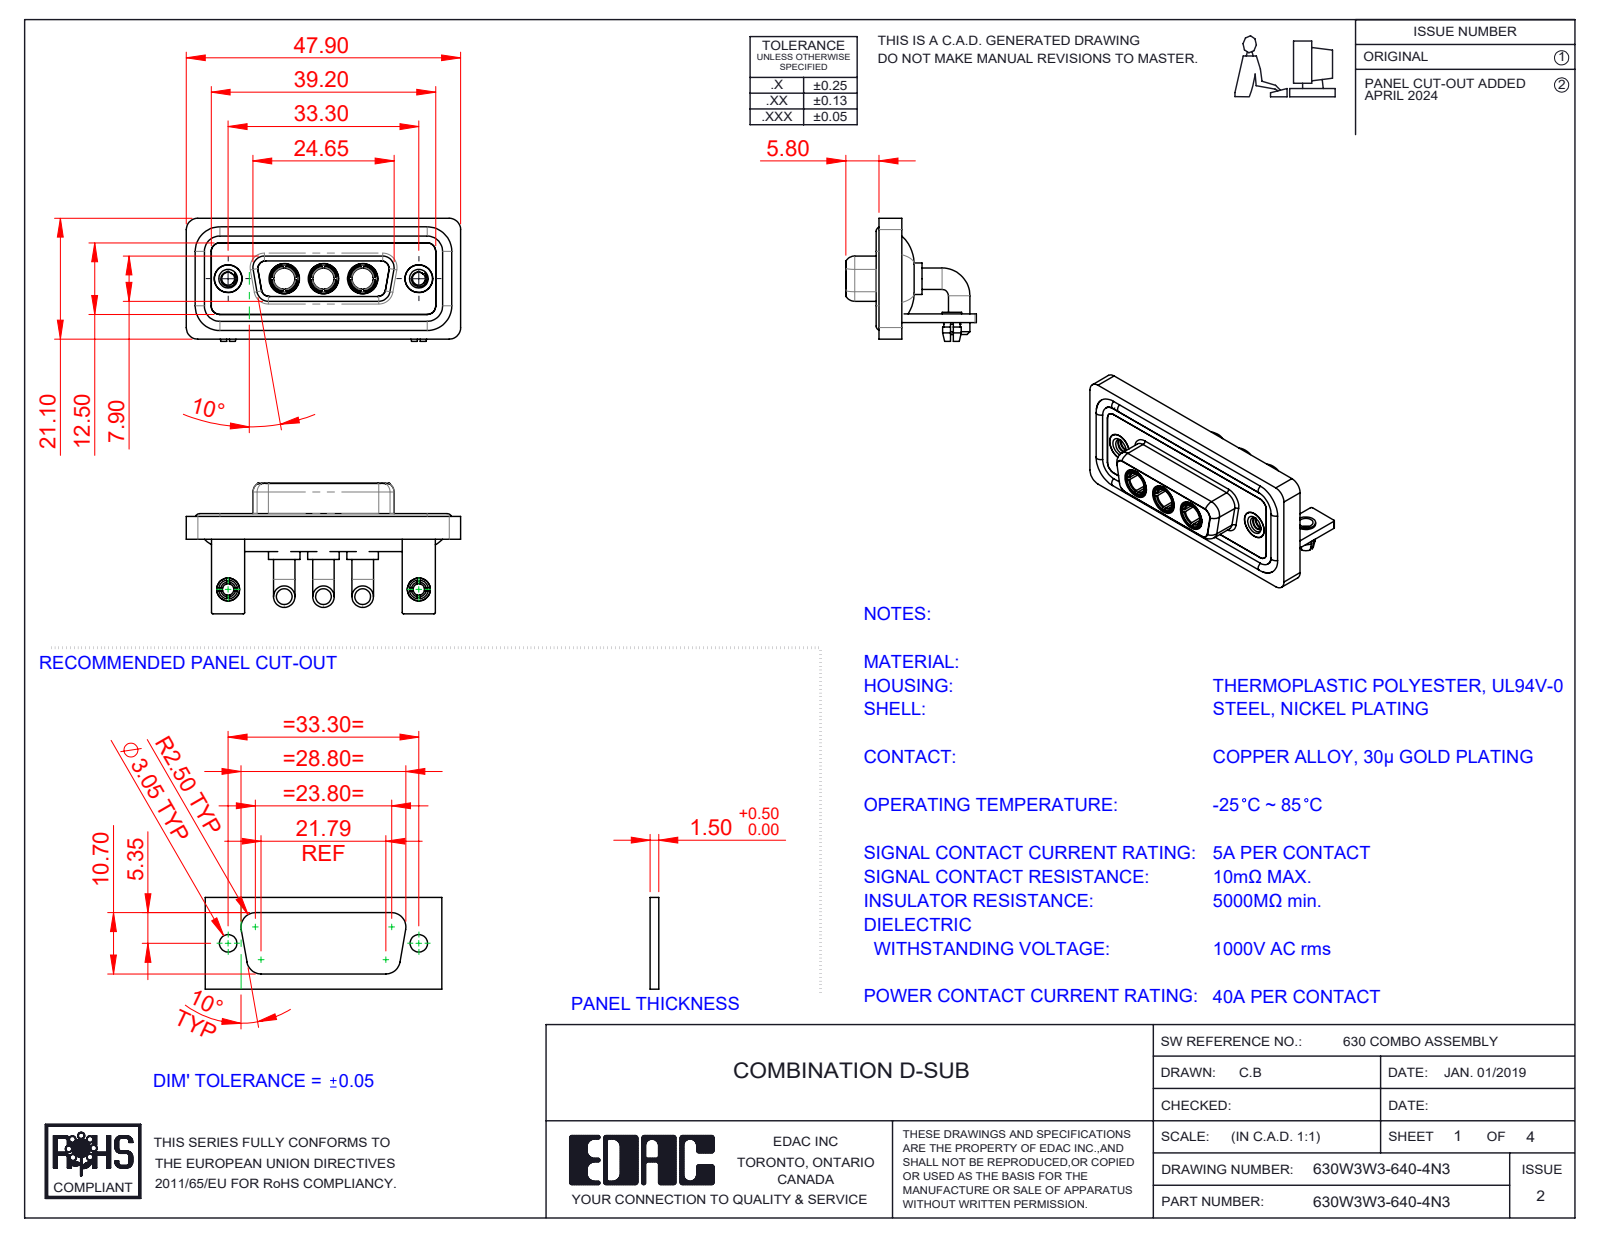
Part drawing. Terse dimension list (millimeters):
name: 630Combo Waterproof Housing_15 Contacts; 630Combo Shell Front_15 Contacts; Power Socket_40A RA; 630Combo Threaded Rivet_2 (+5 more)
written by: SolidWorks 2023 (CONFIG_CONTROL_DESIGN)
unit: mm
bodies: 17 solids, 760 faces (260 planar, 319 cylindrical, 181 other)
size: 47.9 × 22.8 × 21.5
volume: 6 801 mm³; area: 11 049 mm²
holes: 5× ⌀4.85, 3× ⌀3.7, 3× ⌀5.3, 2× ⌀2, 2× ⌀2.26, 2× ⌀2.5, 2× ⌀3.2, 2× ⌀4, 2× ⌀4.05, 2× ⌀5
bosses: 6× ⌀3.75, 4× ⌀1.6, 3× ⌀5.5, 3× ⌀5.2, 3× ⌀4.96, 3× ⌀4.75, 2× ⌀4.95, 2× ⌀4.8
rounds: 21× R2, 18× R1.5, 16× R0.25, 12× R1.35, 8× R1.6, 5× R0.5, 4× R0.6, 4× R0.65
face distances: 0.4, 2.9, 1.5, 1.8, 3.7, 1.1, 4.1, 1.6, 2.5, 1.4
hole spacings: 6.85, 9.8, 16.65, 23.5, 33.3, 13.7
